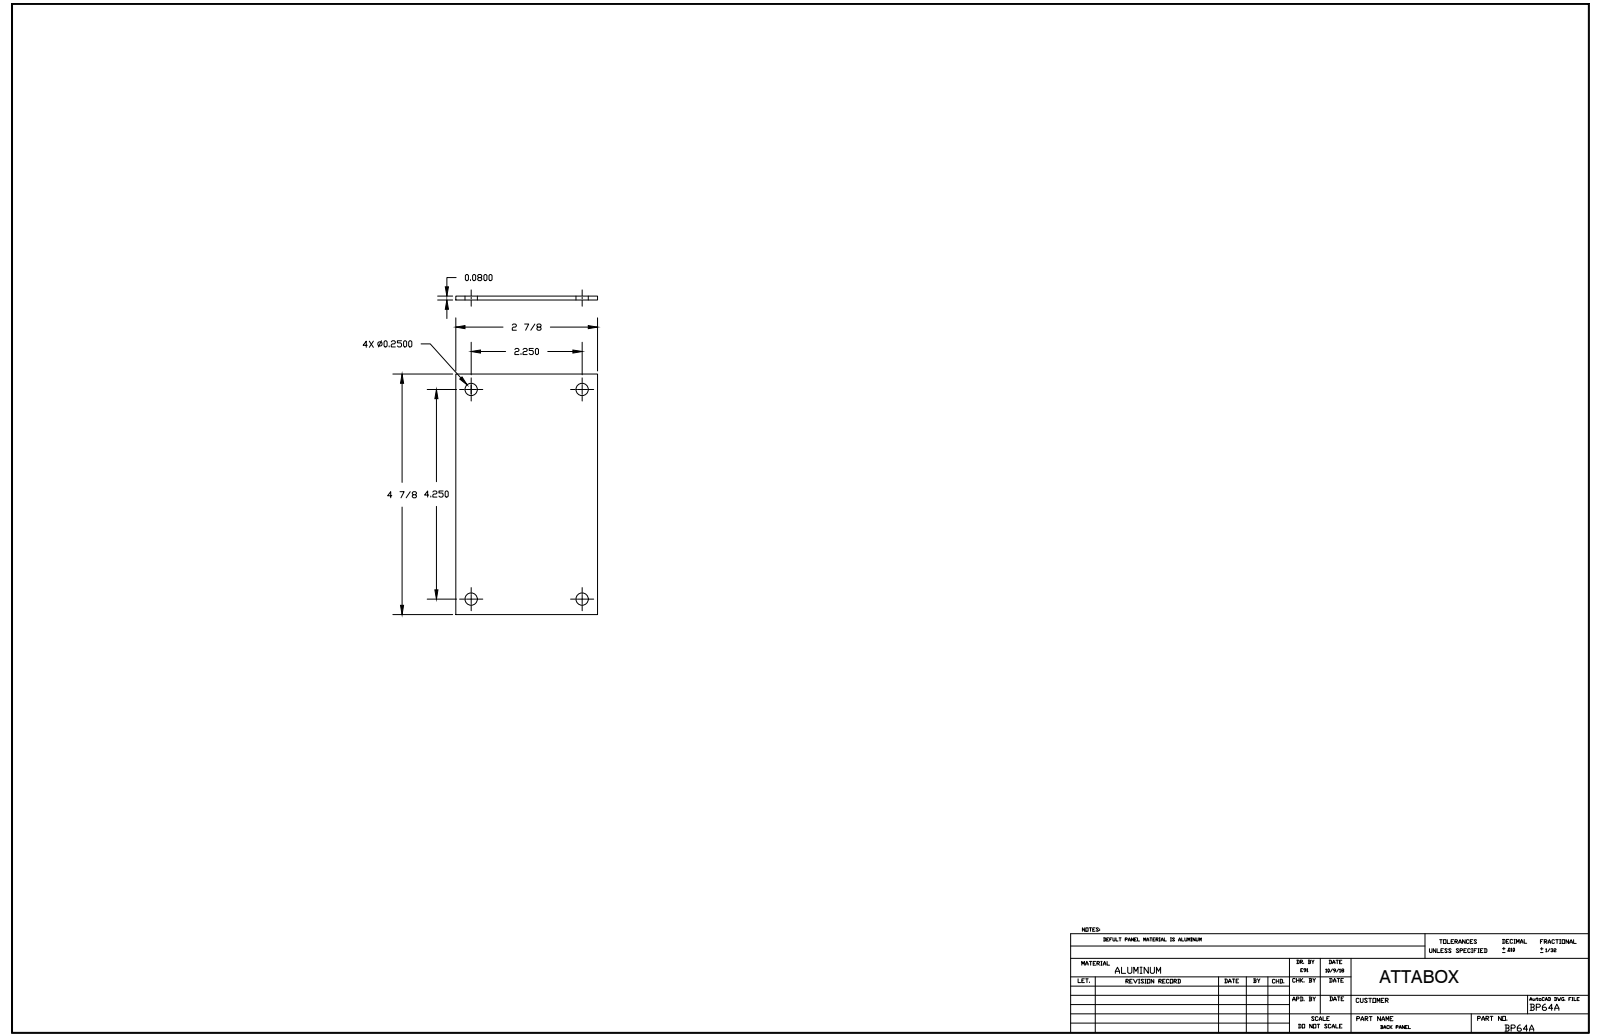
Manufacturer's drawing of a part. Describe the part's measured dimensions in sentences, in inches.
The part is named "BP64AL_STP". Its 3-D file was written by "Autodesk Inventor 2014 (AUTOMOTIVE_DESIGN)". It is 1 solid with 10 faces: 6 planar, 4 cylindrical and 0 other. Overall it measures 4.88 by 2.88 by 0.08 inches. Its volume is 1.109 cubic inches and its surface area 29.21 square inches. Round holes: 4 of diameter 0.25. The main face-to-face distances are 0.08, 2.88, 4.88. The hole center spacings are 2.25, 4.25, 4.809.
